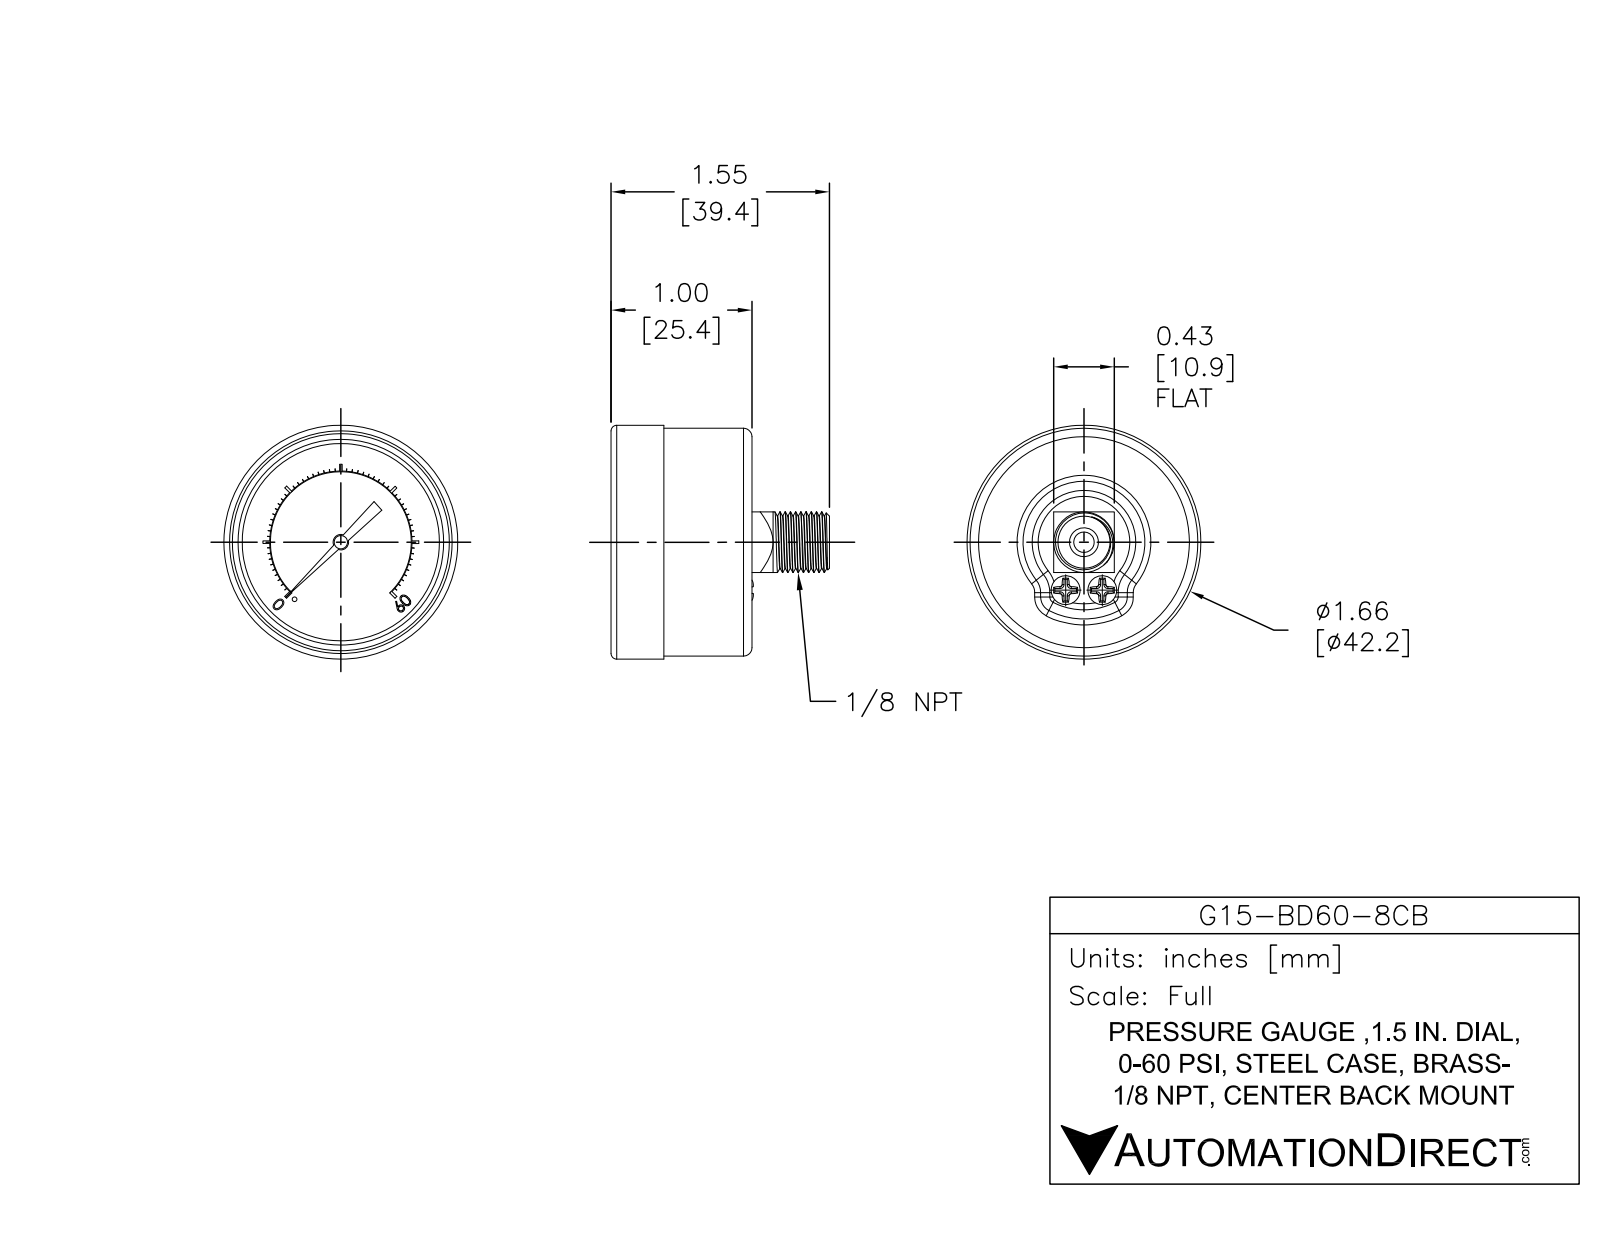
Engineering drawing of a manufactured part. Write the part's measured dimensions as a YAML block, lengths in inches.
part_name: "G15-BD60-8CB"
step_written_by: "SolidWorks 2021 (AUTOMOTIVE_DESIGN)"
units: inches
bodies: {solids: 1, faces: 415, planar: 266, cylindrical: 85, other: 64}
overall_size: [1.66, 1.66, 1.55]
volume: 1.676
surface_area: 12.02
round_holes:
  - {diameter: 0.145, count: 1}
  - {diameter: 1.4, count: 1}
round_bosses_or_shafts:
  - {diameter: 0.205, count: 2}
  - {diameter: 1.66, count: 1}
  - {diameter: 1.617, count: 1}
  - {diameter: 0.43, count: 1}
  - {diameter: 0.086, count: 1}
  - {diameter: 0.06, count: 1}
  - {diameter: 0.033, count: 1}
partial_cylinders:
  - {radius: 0.06, count: 4}
  - {radius: 0.015, count: 2}
  - {radius: 0.048, count: 1}
  - {radius: 0.5, count: 1}
  - {radius: 0.505, count: 1}
face_to_face_distances: [0.71, 0.43, 0.1, 0.61, 0.96, 0.86, 0.25, 0.04, 0.625, 0.525]
